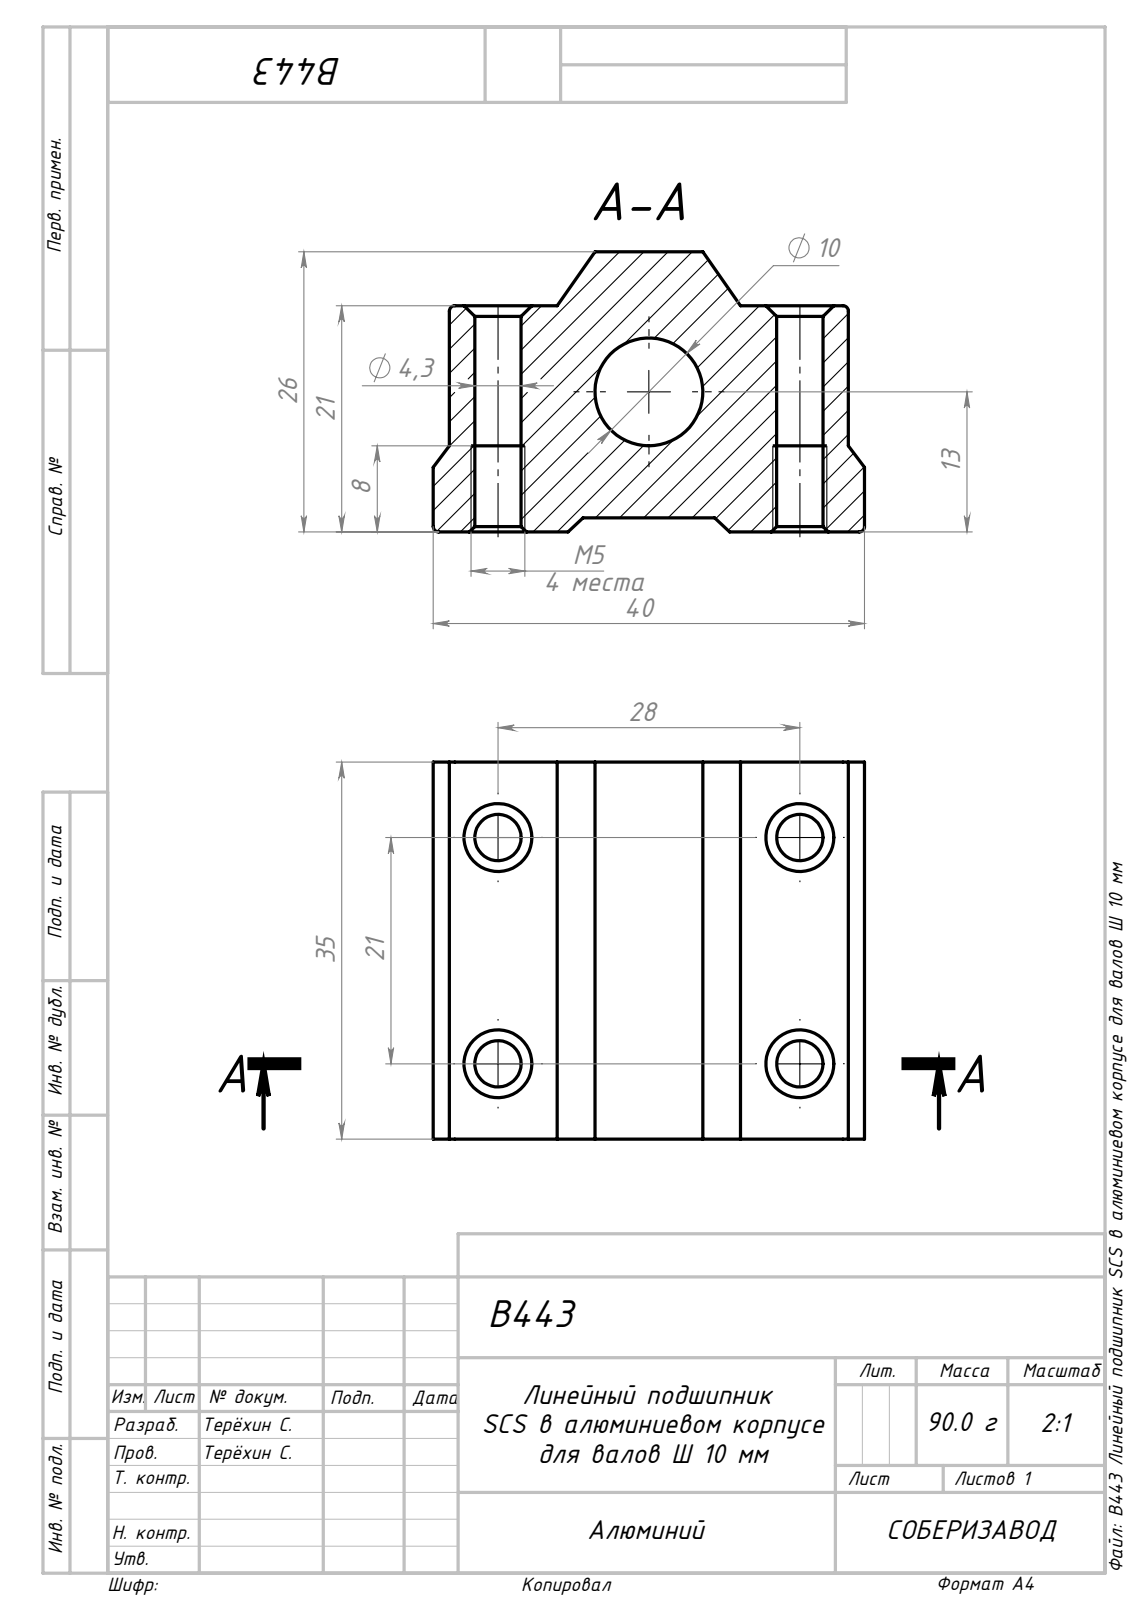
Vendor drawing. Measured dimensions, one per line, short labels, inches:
name: Сборка1; B443 Линейный подшипник SCS в алюминиевом корпусе для валов Ø 10 мм_SCS10UU
written by: SolidWorks 2024 (AUTOMOTIVE_DESIGN)
unit: in
bodies: 1 solid, 48 faces (18 planar, 14 cylindrical, 16 other)
size: 1.575 × 1.378 × 1.024
volume: 1.566 in³; area: 12.4 in²
holes: 4× ⌀0.169, 1× ⌀0.394
rounds: 4× R0.02
face distances: 1.378, 0.827, 1.457, 0.051, 0.776, 0.059, 1.516, 1.024, 0.972, 0.197
hole spacings: 0.827, 1.102, 1.378
